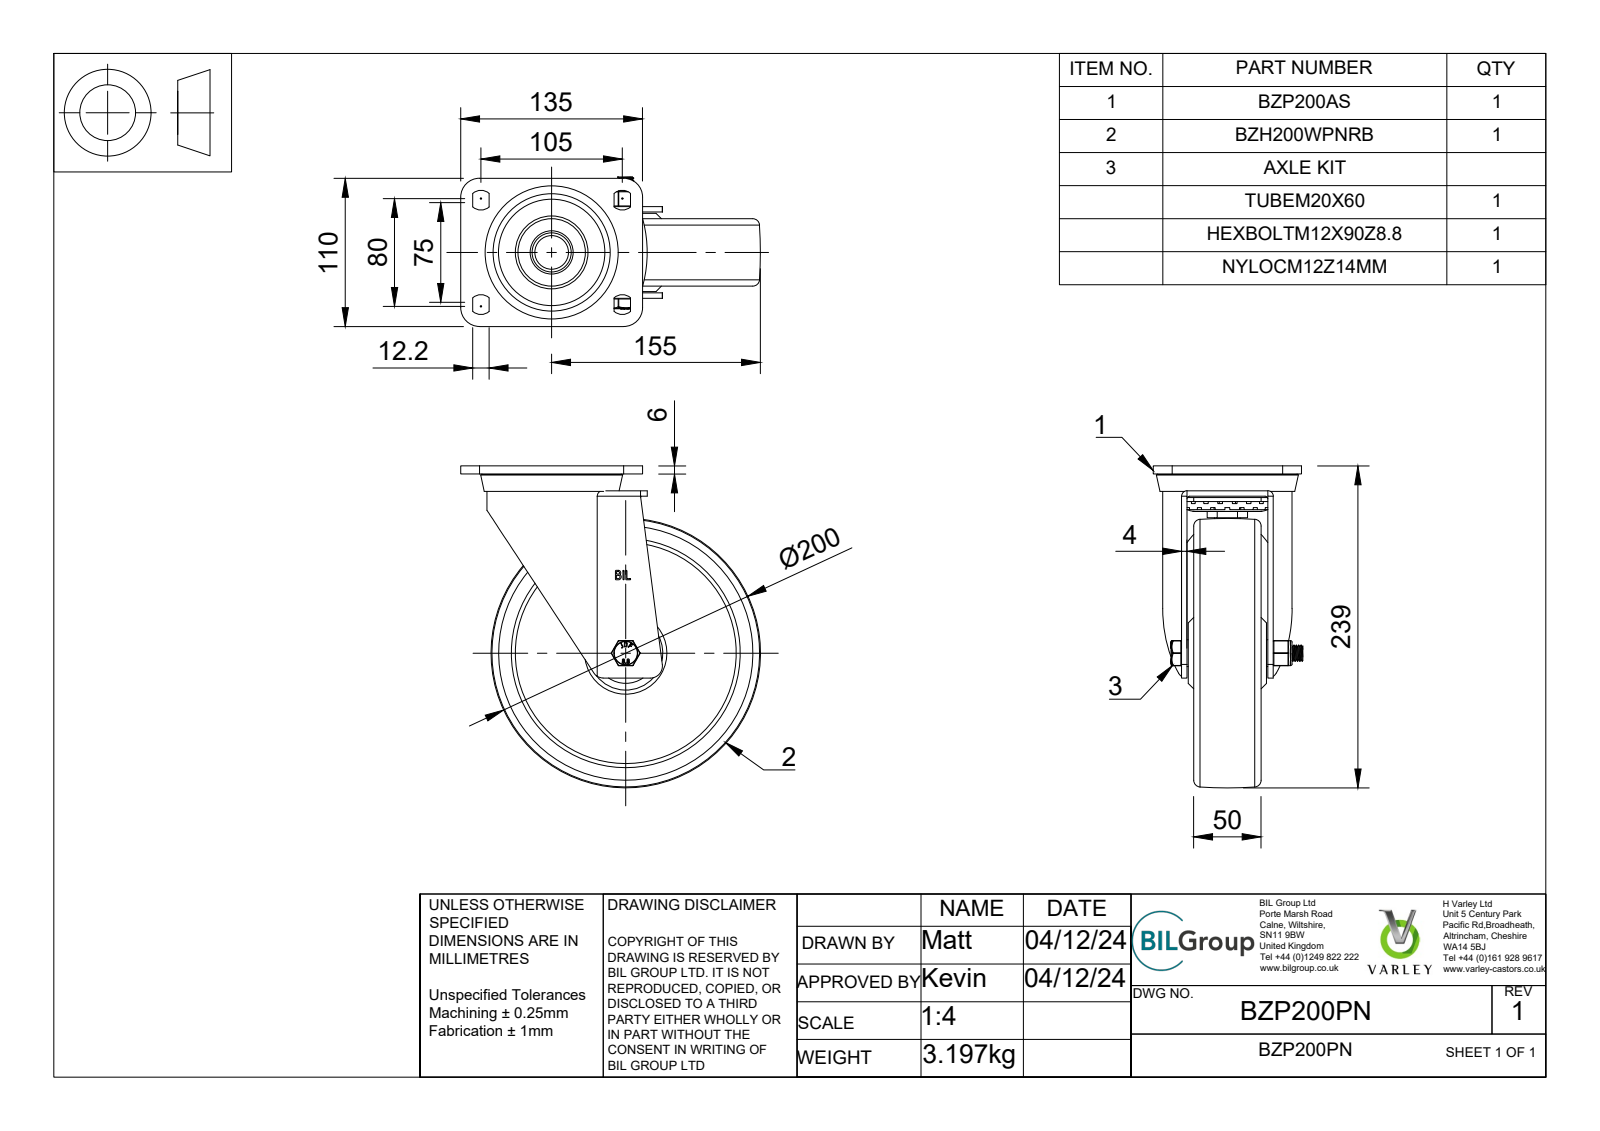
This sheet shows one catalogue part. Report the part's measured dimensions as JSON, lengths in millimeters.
{"part_name": "BZP200PN v4; BZP200AS v1; ZINC PLATED, PRESSED STEEL TOP PLATE; ZINC PLATED, PRESSED STEEL TOP PLATE Geometry (+8 more)", "step_written_by": "Autodesk Translation Framework v13.20.0.188 (AP242_MANAGED_MODEL_BASED_3D_ENGINEERING_MIM_LF)", "units": "millimeters", "bodies": {"solids": 22, "faces": 694, "planar": 405, "cylindrical": 200, "other": 89}, "overall_size": [239, 222.5, 111], "volume_mm3": 1096000, "surface_area_mm2": 343691, "round_holes": [[30, 2], [12, 1], [12.2, 1], [12.5, 1], [14, 1], [19, 1], [20, 1], [20.5, 1], [32, 1], [36, 1], [88, 1], [170, 1]], "round_bosses_or_shafts": [[5, 10], [103.5, 1], [96, 1], [83, 1], [55, 1], [50, 1], [29.5, 1], [29, 1]], "partial_cylinders_radius": [[0.5, 18], [9.09, 8], [0.47, 4], [0.9, 4], [2, 4], [14, 4], [0.89, 2], [0.89, 2]], "face_to_face_distances": [4, 9, 55, 11, 5, 59, 26.5, 6, 19.5, 24.5]}
